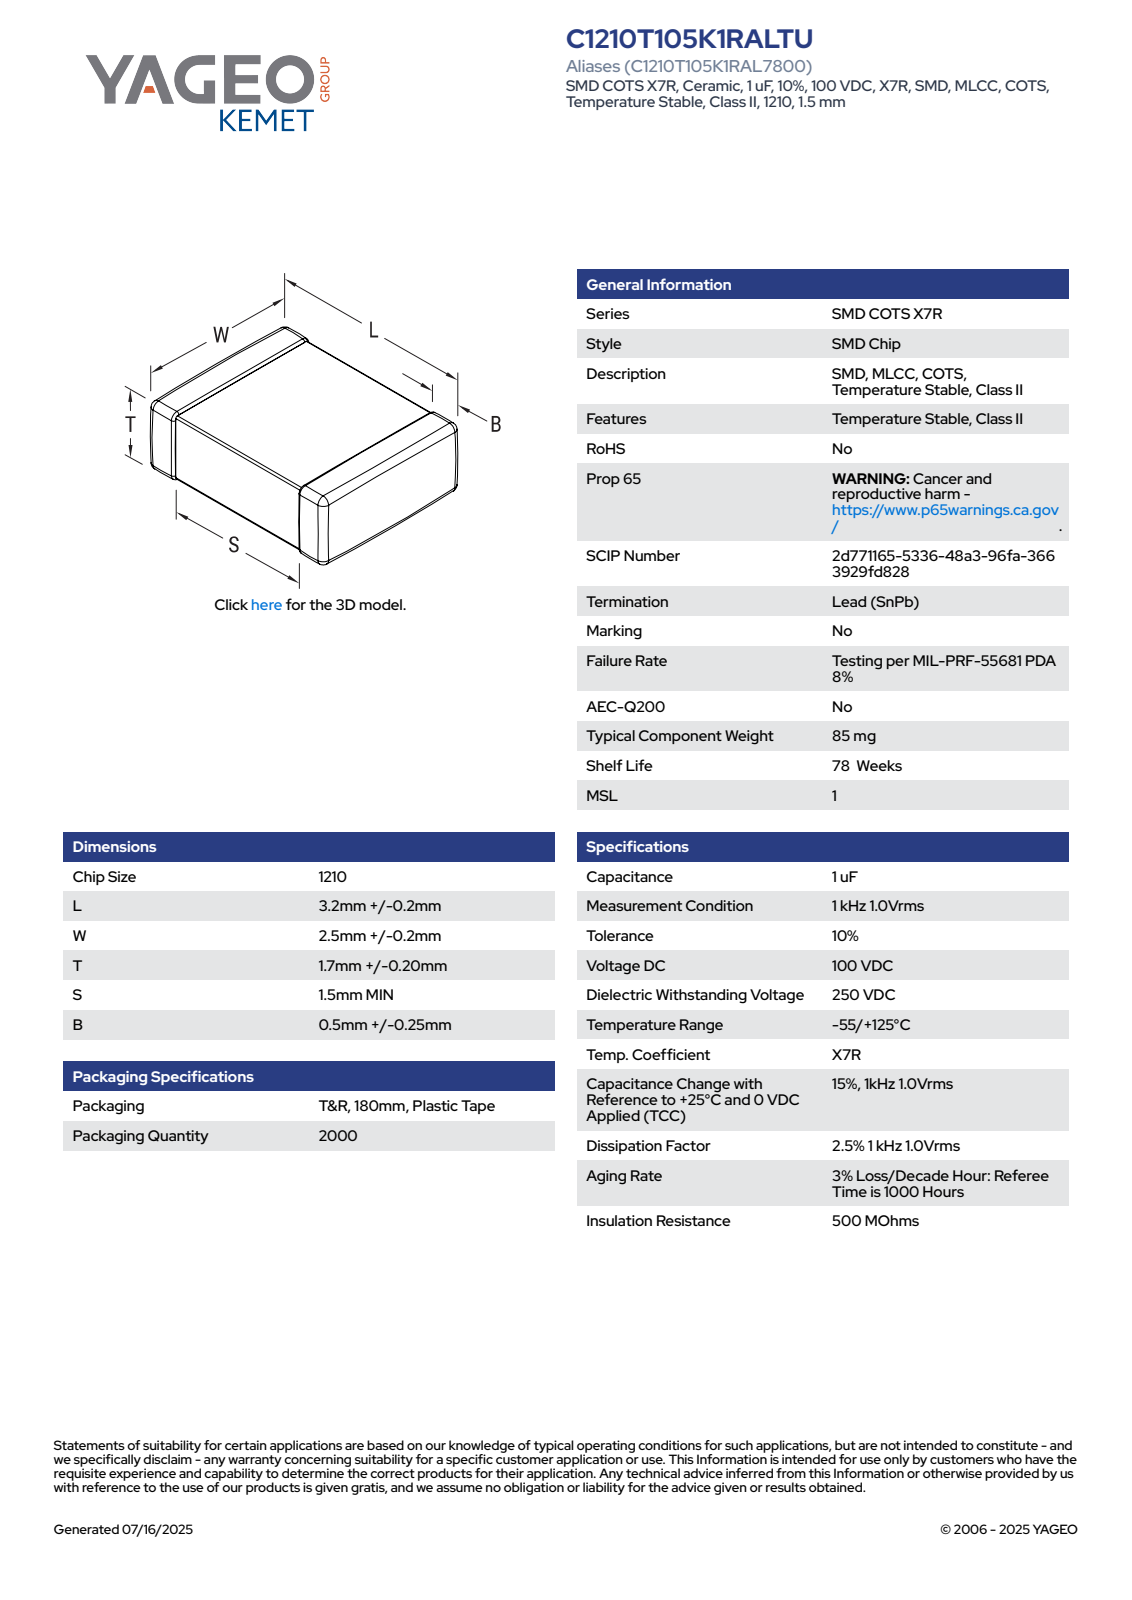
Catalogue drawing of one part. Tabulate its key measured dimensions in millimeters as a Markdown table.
| quantity | value |
| --- | --- |
| part name | CCSM_STD_1210_L3.4W2.7T1.9S1.7B0.75 |
| STEP written by | SolidWorks 2021 (AUTOMOTIVE_DESIGN) |
| units | millimeters |
| bodies | 4 solids, 125 faces (71 planar, 38 cylindrical, 16 other) |
| overall size | 3.4 × 2.7 × 1.9 |
| volume | 16 mm³ |
| surface area | 41 mm² |
| main face-to-face distances | 1.84, 1.78, 3.4, 2.64, 1.9, 2.58, 2.7, 1.85, 1.79, 0.4 |
